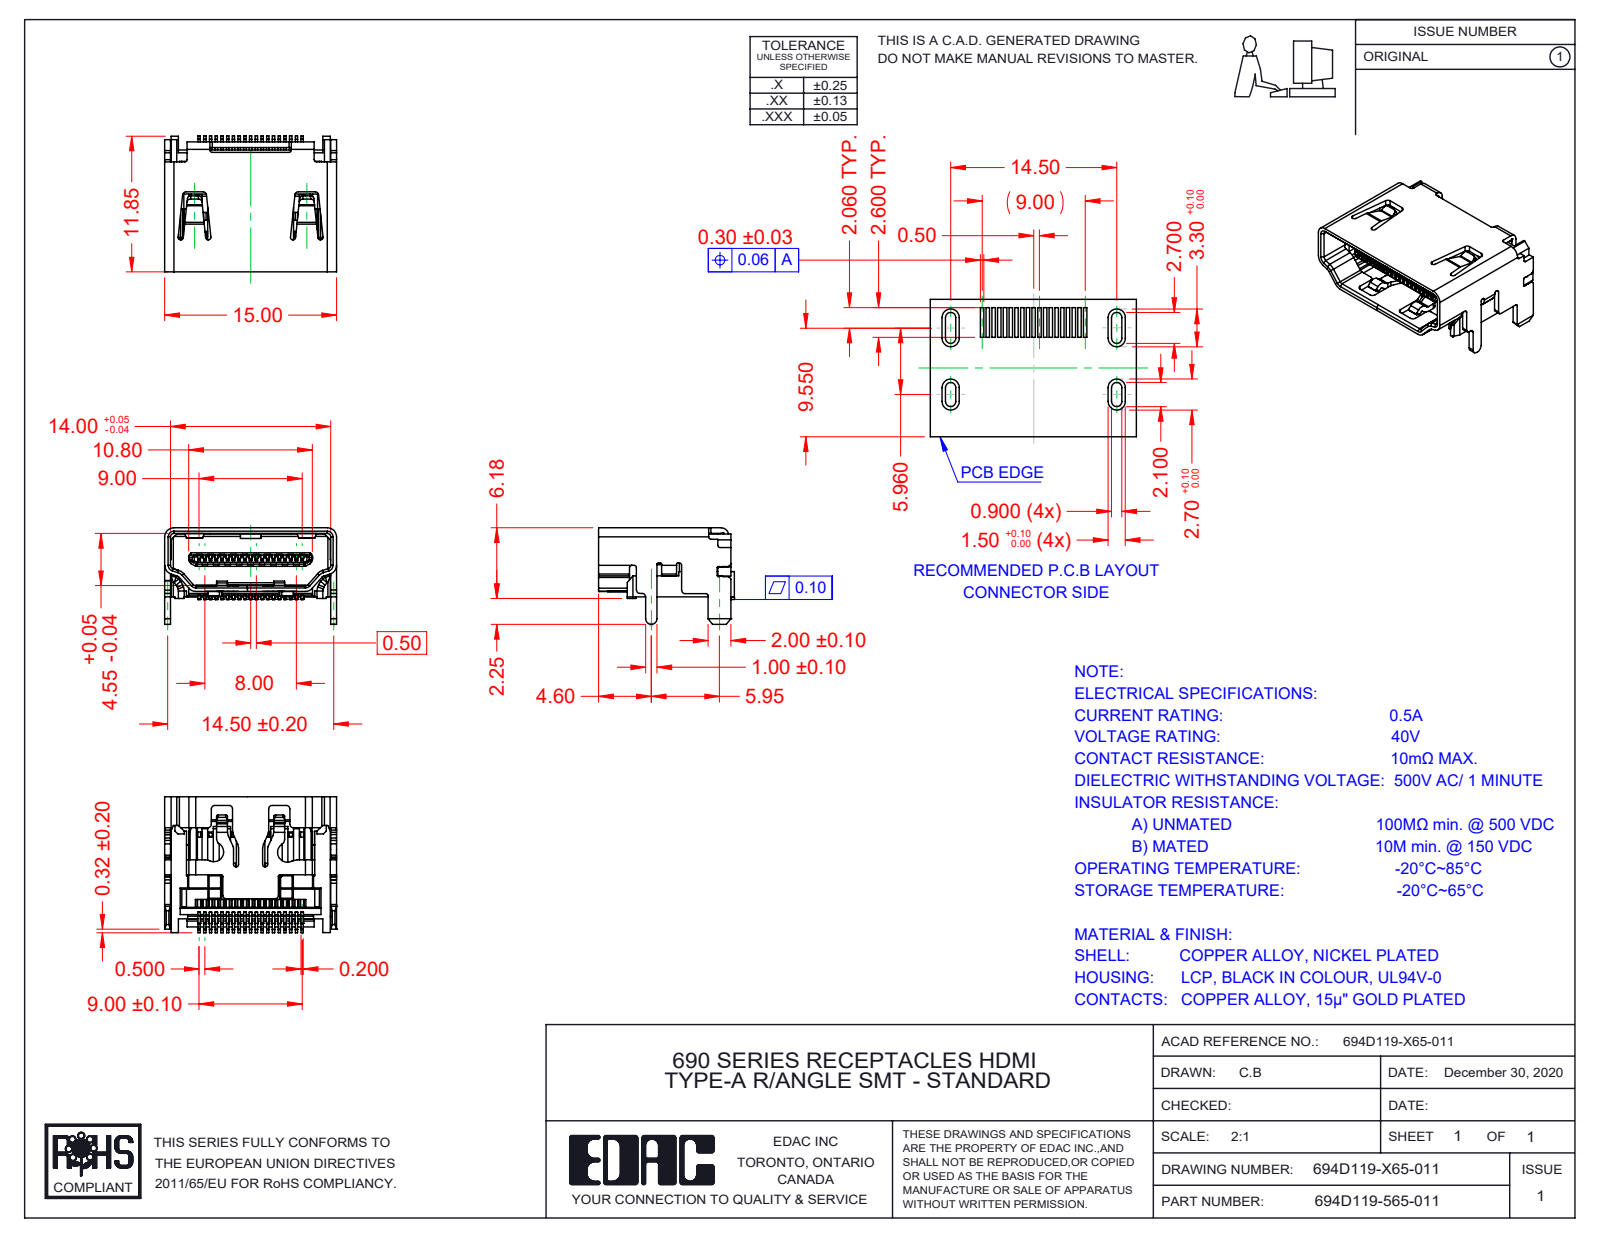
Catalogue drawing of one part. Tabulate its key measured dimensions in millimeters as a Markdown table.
| quantity | value |
| --- | --- |
| part name | 694D119-165-011; Insulator 694D119-X65-011; Shell 694D119-X65-011 |
| STEP written by | SolidWorks 2020 (AUTOMOTIVE_DESIGN) |
| units | millimeters |
| bodies | 2 solids, 1694 faces (1301 planar, 359 cylindrical, 34 other) |
| overall size | 15 × 11.87 × 8.43 |
| volume | 451 mm³ |
| surface area | 1 558 mm² |
| partial cylindrical surfaces (radius × count) | 0.2 × 105, 0.3 × 29, 0.13 × 18, 0.15 × 15, 1 × 10, 0.22 × 8, 0.8 × 8, 0.5 × 7 |
| main face-to-face distances | 0.5, 0.51, 14.5, 4.55, 0.7, 1, 5.05, 3.85, 1.7, 5.06 |
